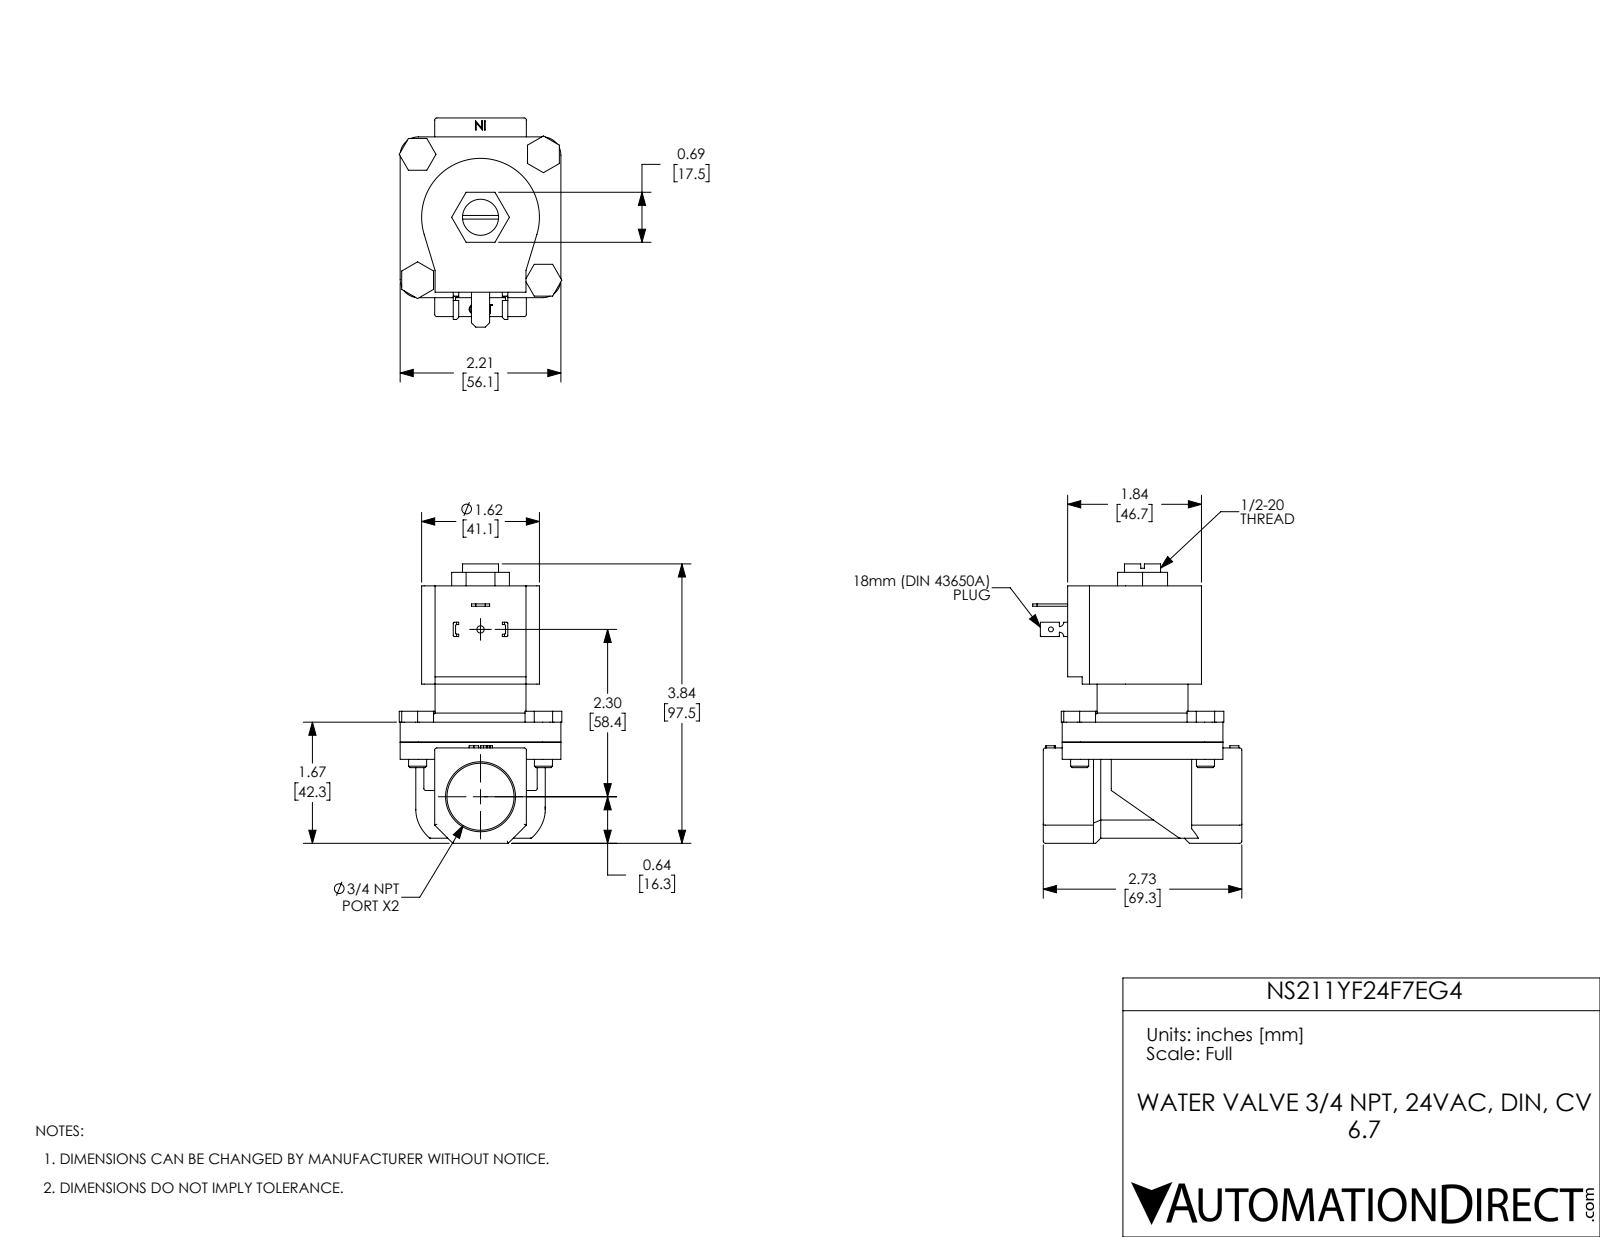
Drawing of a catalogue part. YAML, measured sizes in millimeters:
part_name: "NS211YF24F7EG5"
step_written_by: "SolidWorks 2017 (AUTOMOTIVE_DESIGN)"
units: millimeters
bodies: {solids: 11, faces: 332, planar: 198, cylindrical: 99, other: 35}
overall_size: [97.5, 73, 56.8]
volume: 161500
surface_area: 41390
round_holes:
  - {diameter: 6.4, count: 4}
  - {diameter: 1.7, count: 1}
  - {diameter: 2.5, count: 1}
  - {diameter: 12.6, count: 1}
  - {diameter: 13, count: 1}
  - {diameter: 23.4, count: 1}
  - {diameter: 29.3, count: 1}
round_bosses_or_shafts:
  - {diameter: 6.3, count: 4}
  - {diameter: 31.8, count: 1}
partial_cylinders:
  - {radius: 0.8, count: 15}
  - {radius: 0.4, count: 8}
  - {radius: 6.4, count: 4}
  - {radius: 1.5, count: 2}
  - {radius: 20.6, count: 1}
  - {radius: 22.6, count: 1}
face_to_face_distances: [7, 54.6, 47.6, 12.1, 44.1, 56.1, 20.3, 13.3, 34.3, 6]
hole_center_spacings: [31.1, 43.9, 62.1, 58.4]
